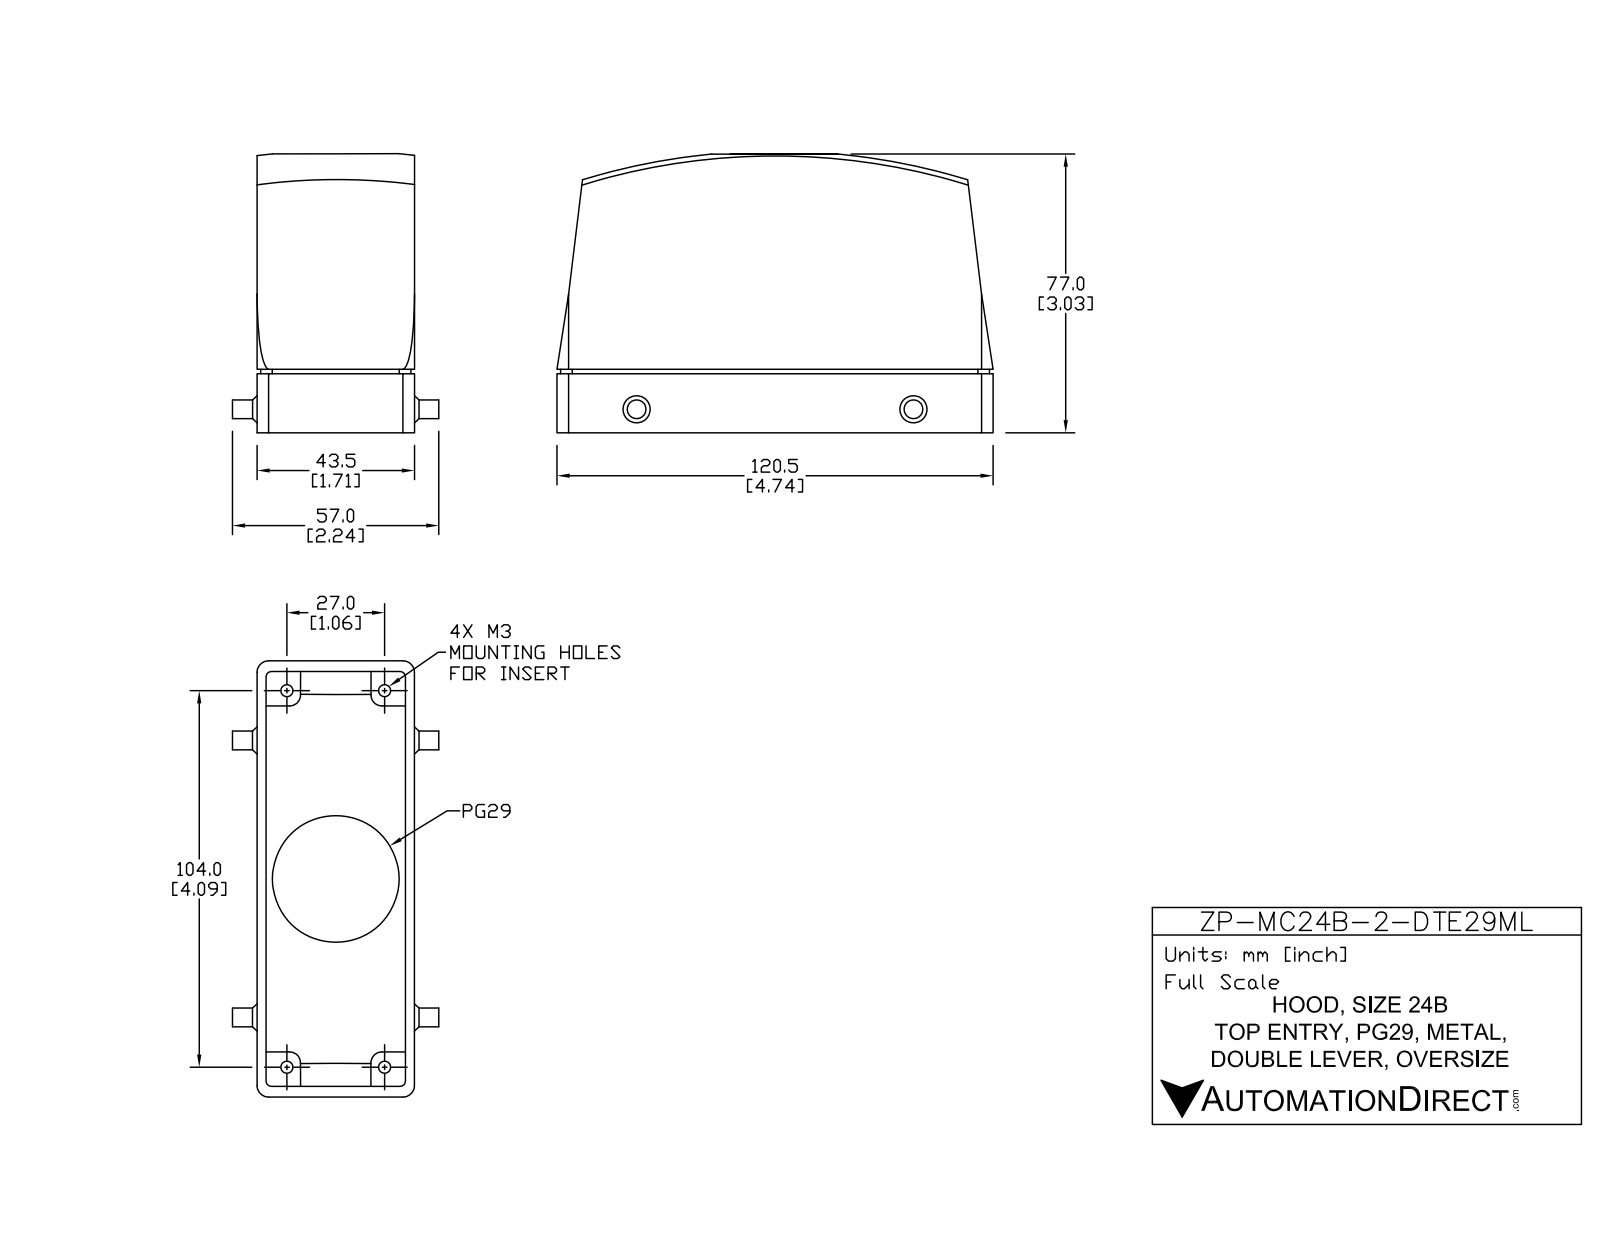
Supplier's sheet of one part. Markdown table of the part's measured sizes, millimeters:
| quantity | value |
| --- | --- |
| part name | ZP-MC24B-2-DTE29ML |
| STEP written by | SolidWorks 2011 (AUTOMOTIVE_DESIGN) |
| units | millimeters |
| bodies | 9 solids, 98 faces (58 planar, 30 cylindrical, 10 other) |
| overall size | 120.5 × 76.74 × 56 |
| volume | 78 712 mm³ |
| surface area | 61 196 mm² |
| round holes (diameter × count) | 3.3 × 4, 35 × 1 |
| round bosses / shafts (diameter × count) | 5.17 × 2 |
| partial cylindrical surfaces (radius × count) | 3.2 × 8, 1.5 × 4, 3 × 4, 0.7 × 1 |
| main face-to-face distances | 2.5, 41, 43.5, 38.5, 9.5, 105.08, 2.96, 12.46, 108.04, 117.54 |
| hole center spacings | 53.72, 27, 104, 107.45 |
